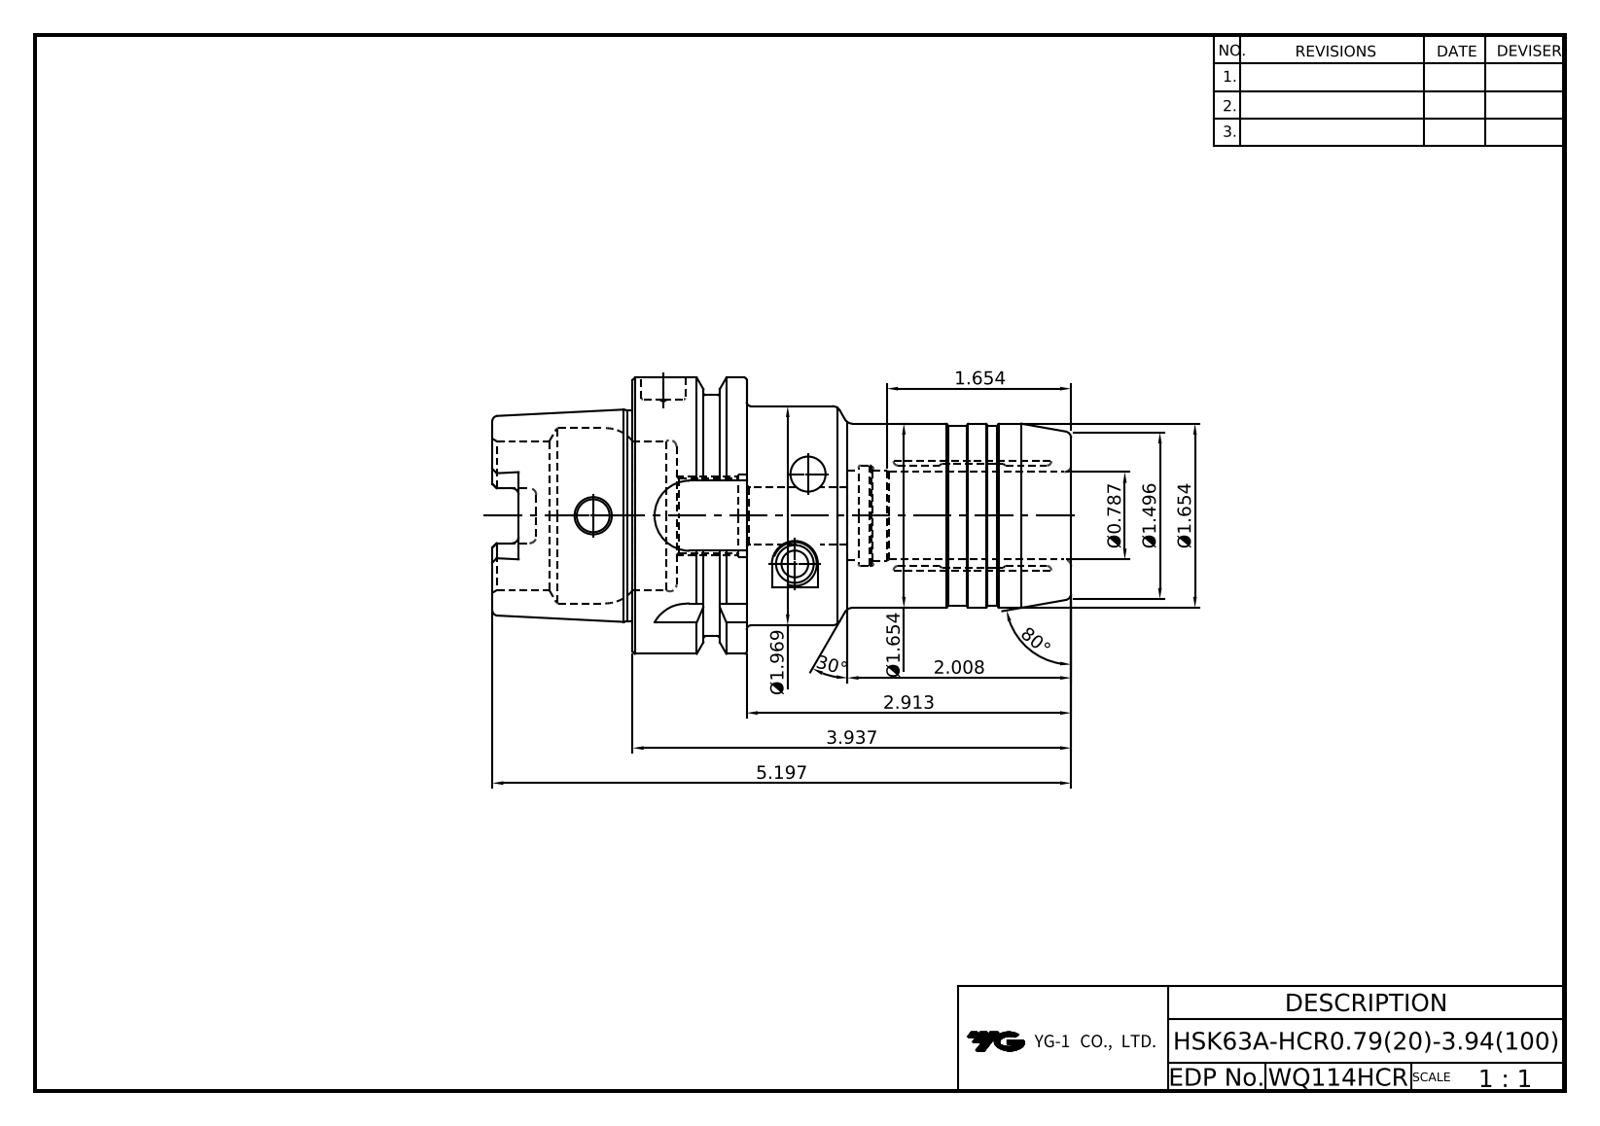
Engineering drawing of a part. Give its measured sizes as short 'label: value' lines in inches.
name: LO-HSK63A-HCR20-100
written by: Autodesk Inventor 2020 (AUTOMOTIVE_DESIGN)
unit: in
bodies: 1 solid, 135 faces (42 planar, 38 cylindrical, 55 other)
size: 5.197 × 2.48 × 2.48
volume: 10.68 in³; area: 55.96 in²
holes: 1× ⌀0.295, 1× ⌀0.394, 1× ⌀0.52, 1× ⌀0.666, 1× ⌀0.748, 1× ⌀0.787, 1× ⌀0.803, 1× ⌀1.339, 1× ⌀1.575
bosses: 1× ⌀2.48, 1× ⌀2.165, 1× ⌀1.969, 1× ⌀1.891, 1× ⌀1.654, 1× ⌀1.614
rounds: 6× R0.059, 4× R0.113, 4× R0.315
face distances: 1.024, 3.937, 2.913, 0.394, 0.63, 3.543, 1.26, 1.654, 2.283, 5.197
